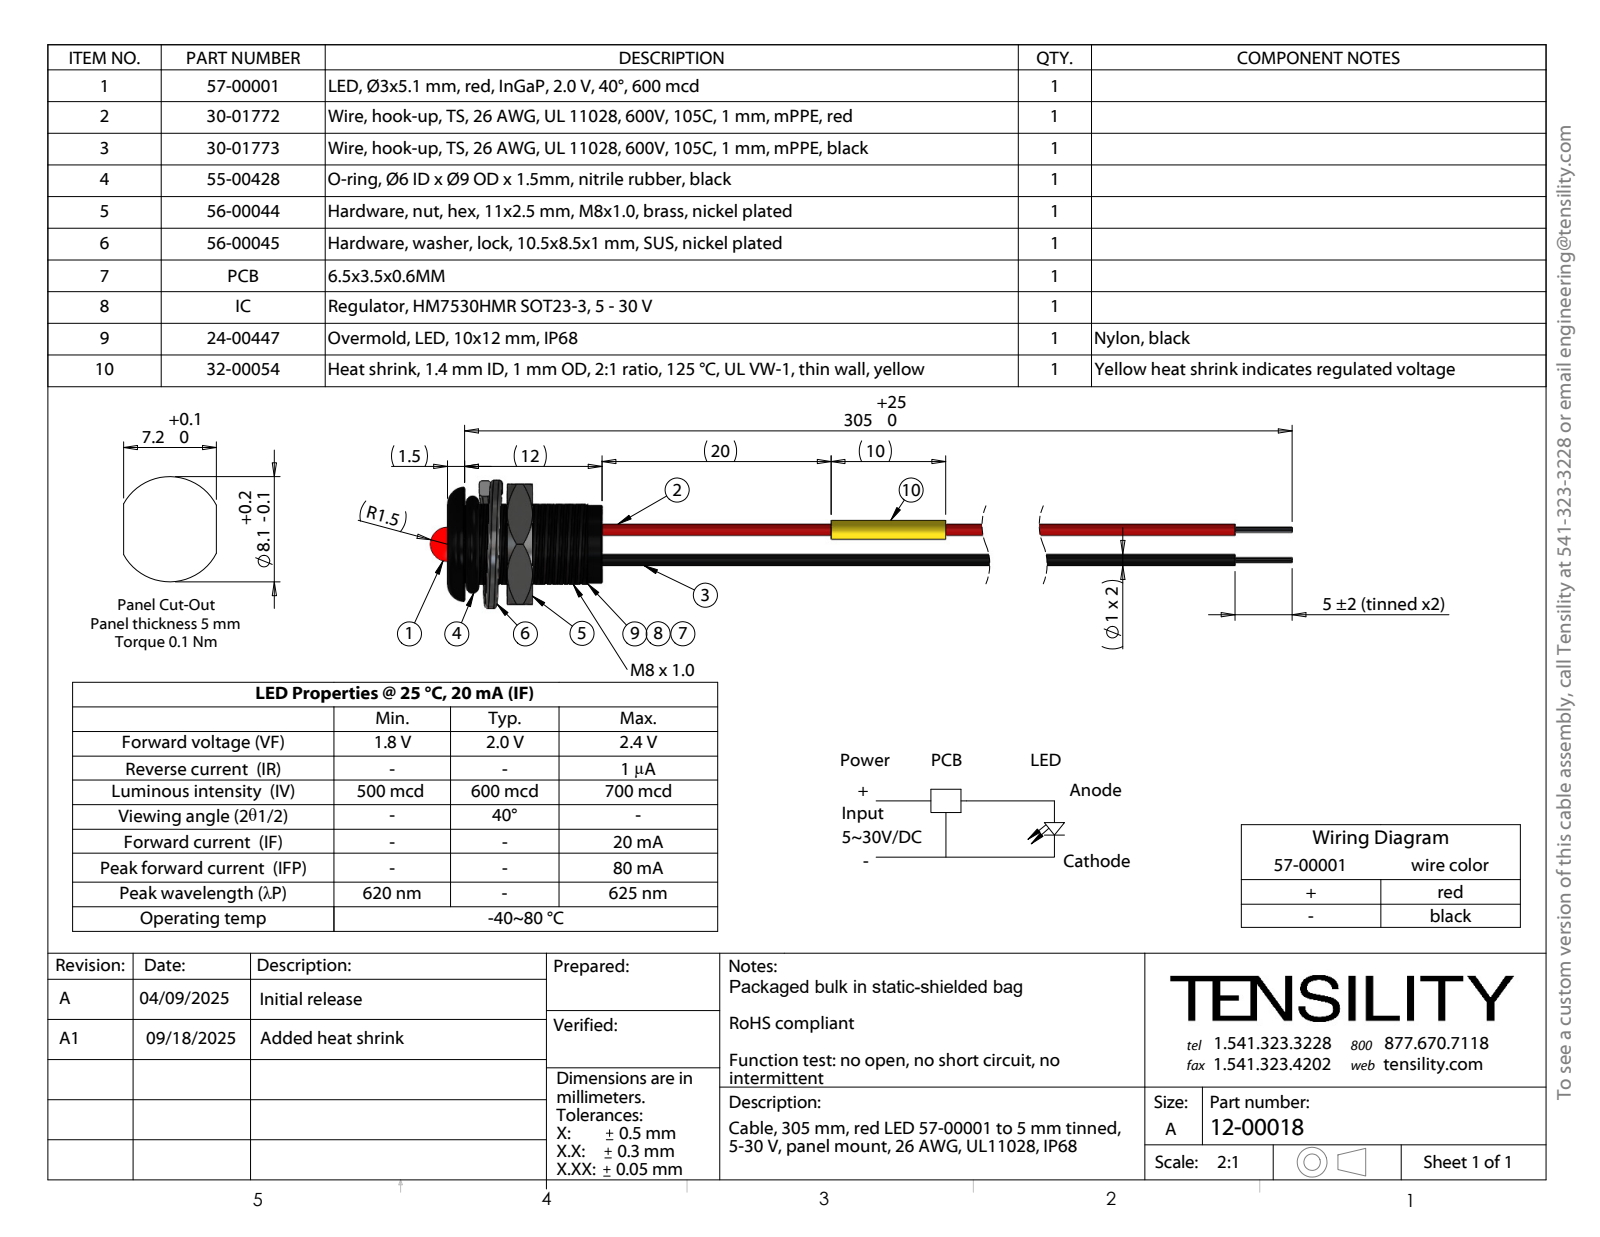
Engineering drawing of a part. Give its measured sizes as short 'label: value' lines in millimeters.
name: 30-01772_stripped and tinned; 30-01773_stripped and tinned; 56-00044; 57-00001_trimmed leads (+4 more)
written by: SolidWorks 2021 (CONFIG_CONTROL_DESIGN)
unit: mm
bodies: 57 solids, 555 faces (186 planar, 246 cylindrical, 123 other)
size: 169.99 × 12.12 × 11.21
volume: 1 005 mm³; area: 5 908 mm²
holes: 2× ⌀1
bosses: 2× ⌀1, 2× ⌀0.5, 1× ⌀6.8, 1× ⌀3
rounds: 1× R3.48, 1× R4
face distances: 1.5, 13.5, 12, 10.5, 5.21, 3.71, 8.29, 7.41, 5.91, 2.2
hole spacings: 0.36, 0.38, 0.33, 2.48, 2.52, 2.43, 2.44, 2.56
